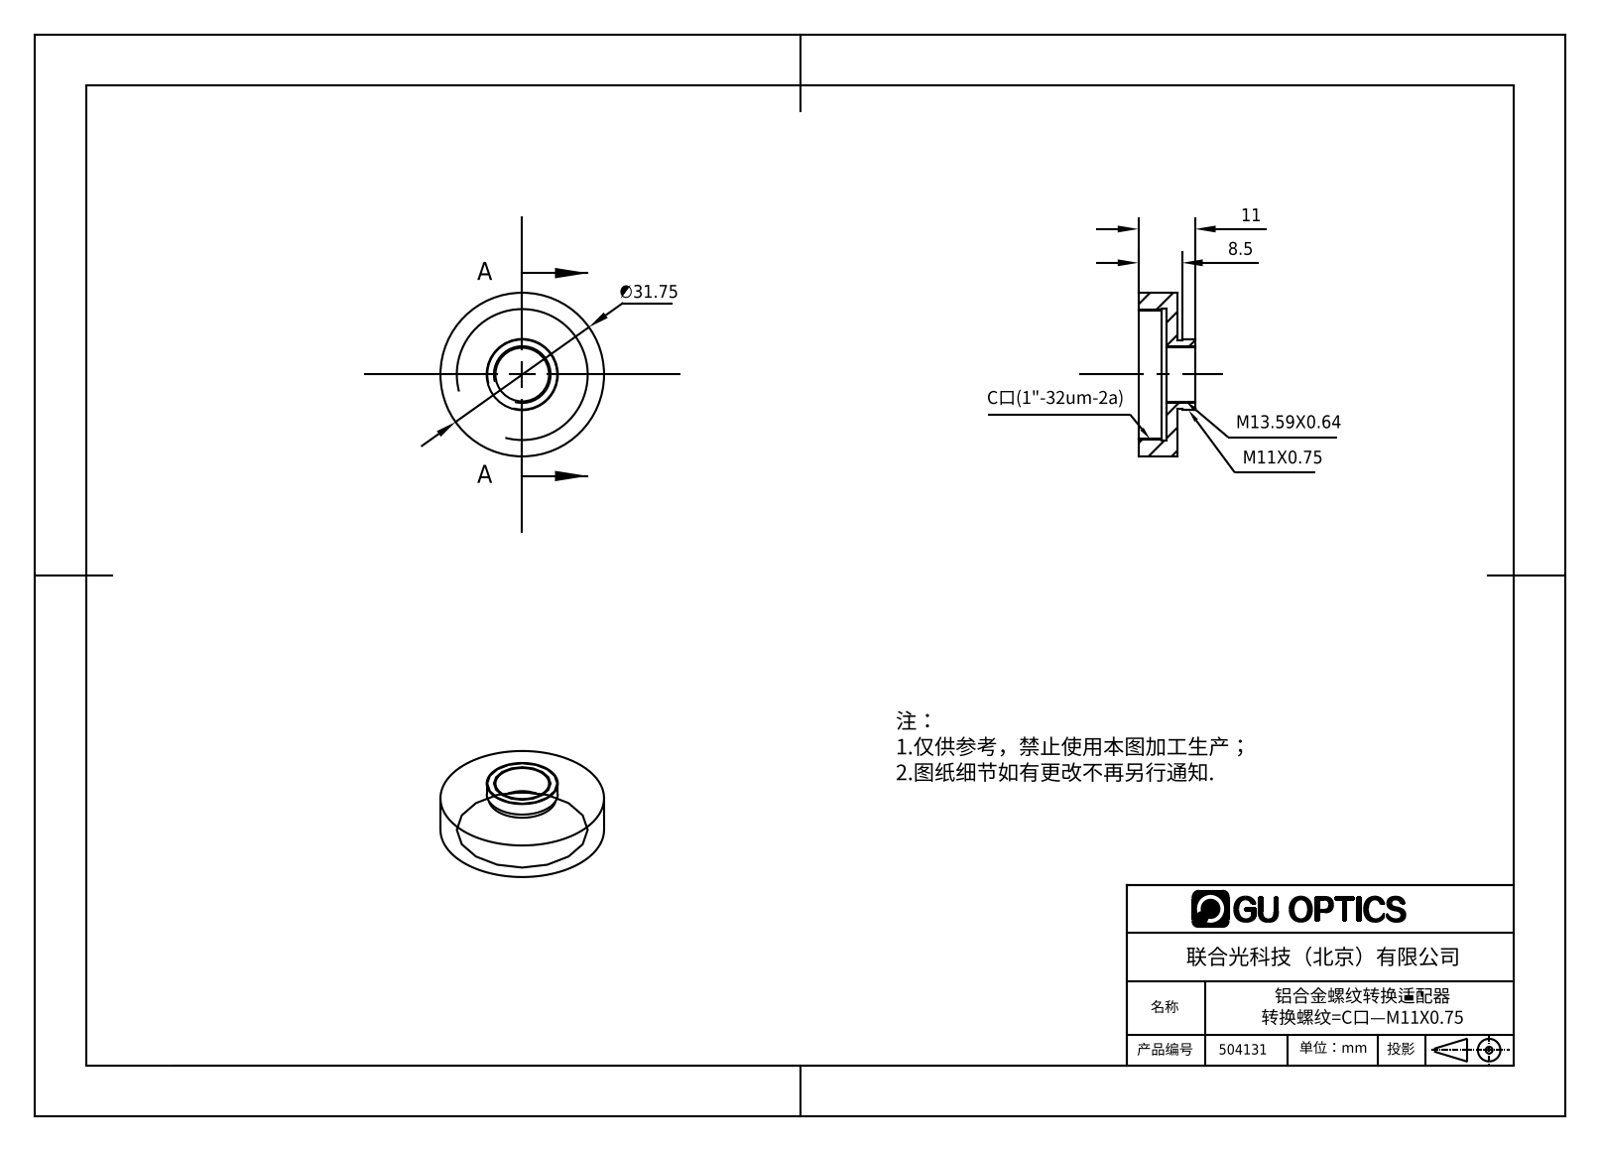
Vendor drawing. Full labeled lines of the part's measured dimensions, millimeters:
Part name (STEP PRODUCT): 504131
STEP written by: SolidWorks 2016 (AUTOMOTIVE_DESIGN)
Units: millimetres
Bodies: 1 solid, 18 faces (6 planar, 12 cylindrical, 0 other)
Overall size (bounding box): 31.75 × 31.75 × 11
Volume: 3 256 mm³ · Surface area: 3 002 mm²
Round holes (diameter × count): ⌀10.4 ×1, ⌀25 ×1, ⌀25.6 ×1
Round bosses / shafts (diameter × count): ⌀31.75 ×1, ⌀13.8 ×1, ⌀13.1 ×1
Main face-to-face distances: 2, 5.5, 7.5, 11, 3.5, 1, 3, 4.5, 6.5, 8.5
